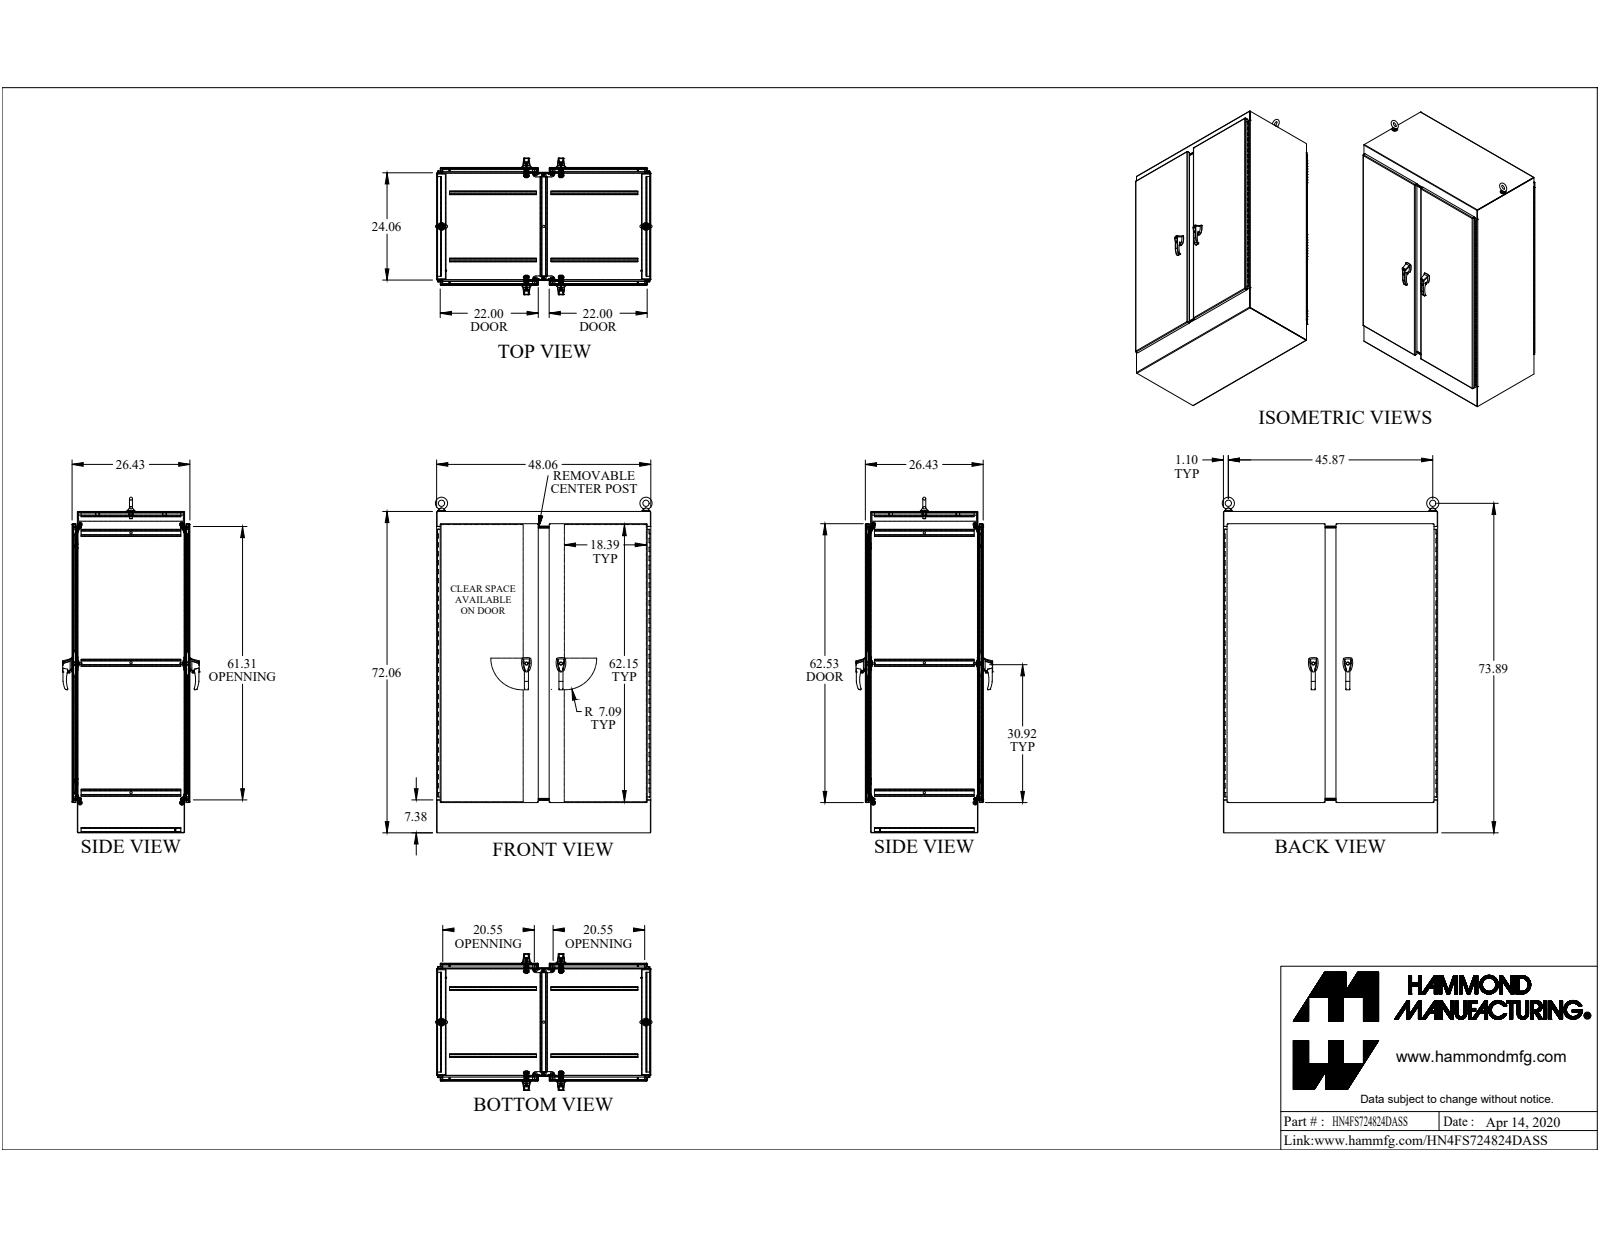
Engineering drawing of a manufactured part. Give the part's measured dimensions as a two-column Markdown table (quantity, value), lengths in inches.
| quantity | value |
| --- | --- |
| part name | HN4FS724824DASS |
| STEP written by | SolidWorks 2019 (CONFIG_CONTROL_DESIGN) |
| units | inches |
| bodies | 187 solids, 5401 faces (2803 planar, 2122 cylindrical, 476 other) |
| overall size | 75.256 × 48.604 × 30.664 |
| volume | 1 697 in³ |
| surface area | 35 739 in² |
| round holes (diameter × count) | 0.304 × 20, 0.25 × 12, 0.35 × 9, 0.313 × 8, 0.201 × 6, 0.257 × 6, 0.28 × 6, 0.281 × 6, 0.313 × 6, 0.39 × 6, 0.413 × 6, 0.11 × 4 |
| round bosses / shafts (diameter × count) | 0.75 × 8, 0.44 × 8, 1 × 6, 0.63 × 6, 0.625 × 6, 0.293 × 6, 0.246 × 6, 0.37 × 5 |
| partial cylindrical surfaces (radius × count) | 0.018 × 64, 0.043 × 60, 0.138 × 48, 0.1 × 46, 0.5 × 46, 0.125 × 42, 0.06 × 39, 0.318 × 34 |
| main face-to-face distances | 0.095, 26.339, 47.965, 26.244, 1.187, 25.152, 26.434, 71.965, 47.87, 48.06 |
| hole center spacings | 6, 46.715, 12, 47.857, 18, 49.702, 24, 52.176 |
